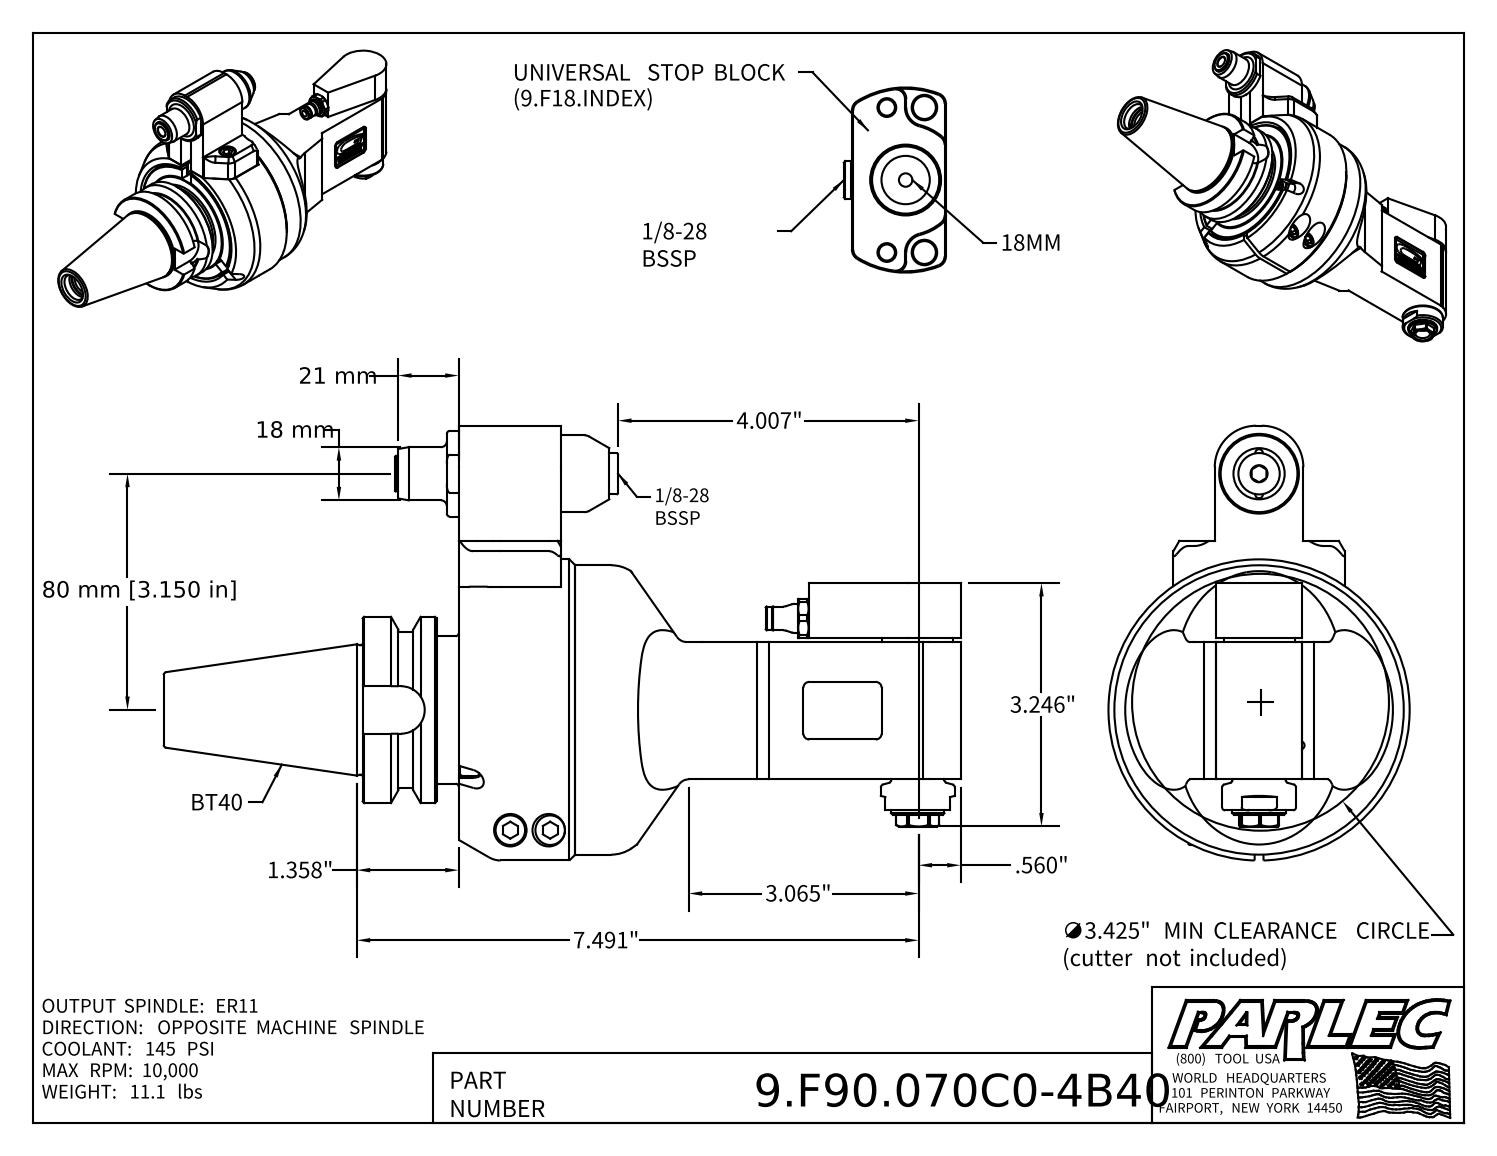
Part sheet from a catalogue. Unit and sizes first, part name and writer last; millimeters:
Units: millimetres
Overall size (bounding box): 269.9 × 147.2 × 102
Round holes (diameter × count): ⌀8.5 ×21, ⌀2.6 ×2, ⌀4.2 ×2, ⌀5 ×2, ⌀10.4 ×2, ⌀11 ×2, ⌀2.5 ×1, ⌀3 ×1, ⌀4 ×1, ⌀6.5 ×1, ⌀7 ×1, ⌀7.5 ×1
Round bosses / shafts (diameter × count): ⌀10 ×4, ⌀6 ×4, ⌀18 ×3, ⌀8 ×2, ⌀2.5 ×2, ⌀102 ×1, ⌀98 ×1, ⌀77 ×1
Partial cylindrical surfaces — rounded edges, fillets, slot ends (radius × count): R2 ×12, R4 ×4, R0.5 ×2, R1 ×2, R3.5 ×2, R5 ×2, R14 ×2, R14.5 ×2
Main face-to-face distances: 32, 0.5, 39.5, 7.5, 8, 29, 7, 65.3, 46.5, 32.5
Hole centre spacings: 38.5, 76.3, 46.3, 54.5, 74, 10.7, 37.3, 77
Volume: 858 400 mm³ · Surface area: 149 600 mm²
Bodies: 5 solids, 552 faces (260 planar, 148 cylindrical, 144 other)
Part name (STEP PRODUCT): 9.F90.070C0-4B40; 9_GA1_348_2 (Type 1, BT40, 80mm); 9FL1ATC; 9BT401ATC (+4 more)
STEP written by: Autodesk Inventor 2022 (AUTOMOTIVE_DESIGN)
